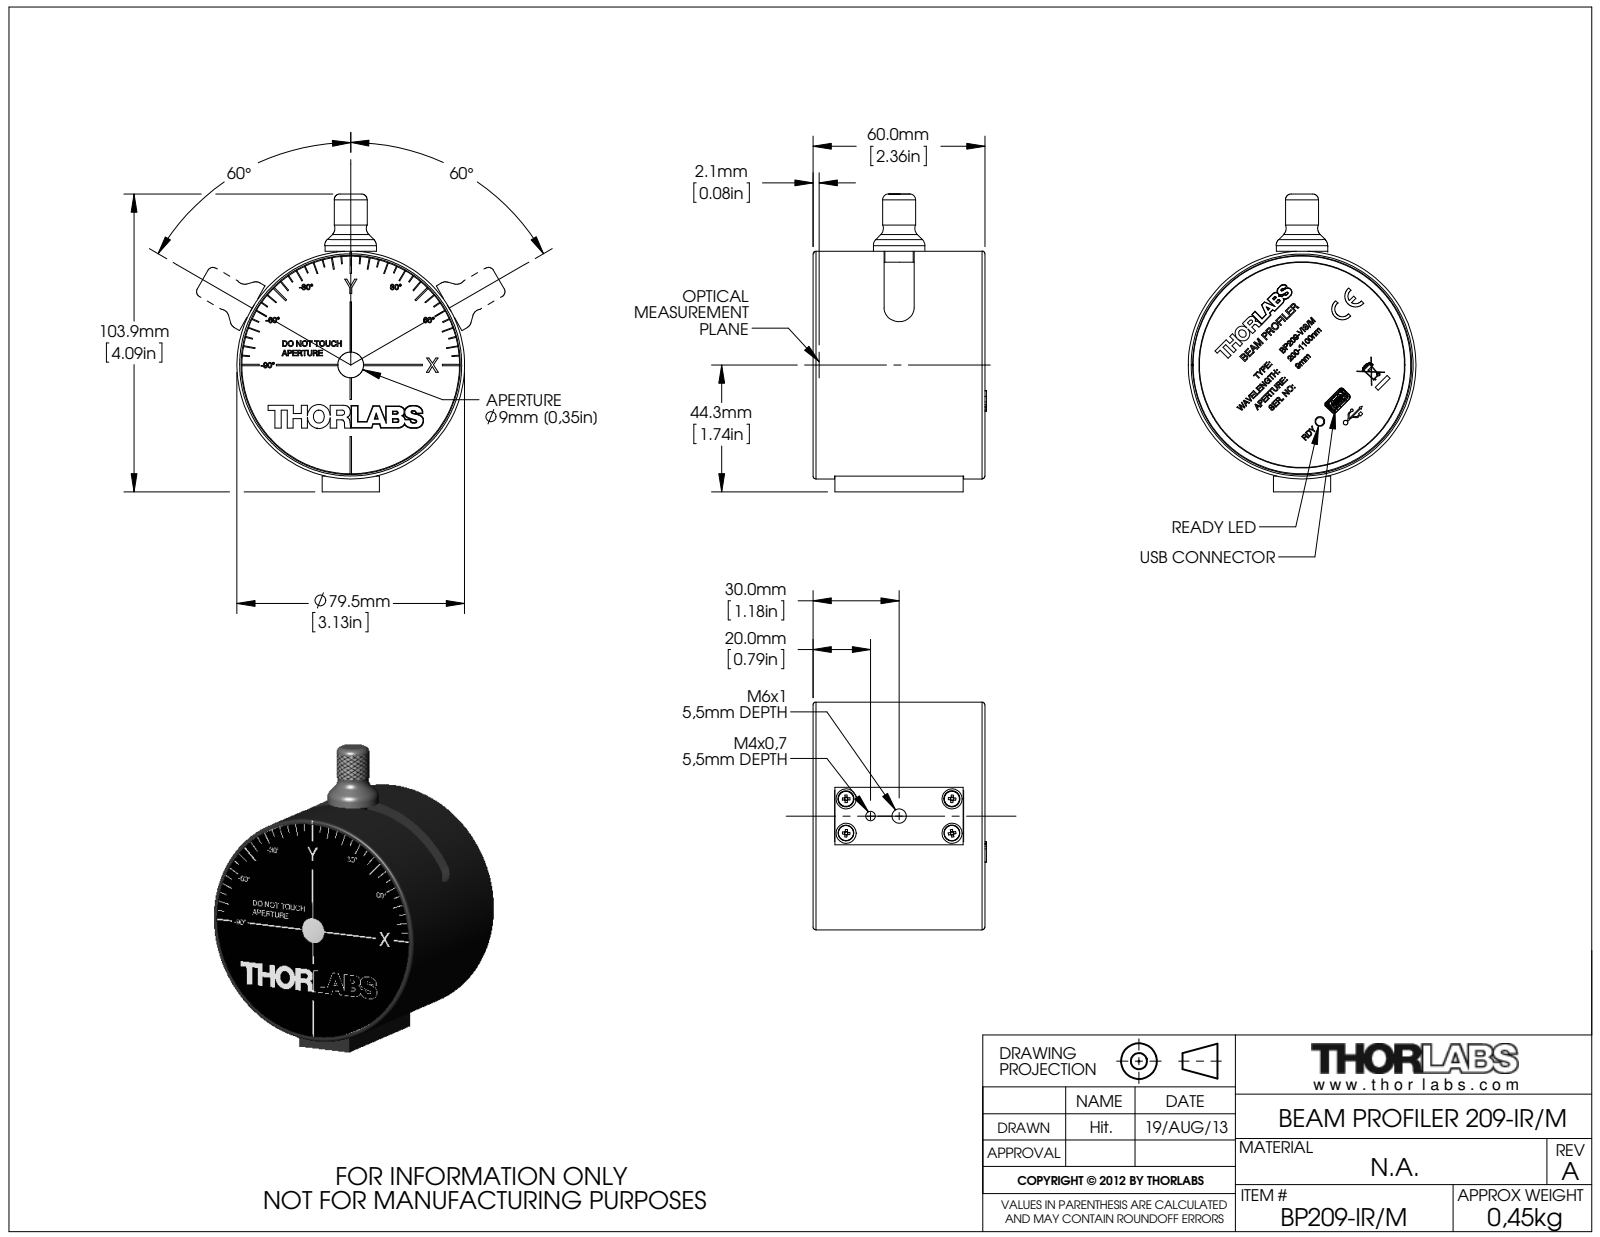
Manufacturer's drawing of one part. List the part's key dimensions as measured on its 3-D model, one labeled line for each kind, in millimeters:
Part name (STEP PRODUCT): 25067-E0W
STEP written by: SolidWorks 2012 (CONFIG_CONTROL_DESIGN)
Units: millimetres
Bodies: 14 solids, 3722 faces (2613 planar, 408 cylindrical, 701 other)
Overall size (bounding box): 103.95 × 79.5 × 60.5
Volume: 98 412 mm³ · Surface area: 99 234 mm²
Round holes (diameter × count): ⌀3.2 ×10, ⌀2.2 ×9, ⌀8 ×8, ⌀1.6 ×6, ⌀6.3 ×6, ⌀5 ×5, ⌀7 ×5, ⌀2.5 ×4, ⌀5.3 ×4, ⌀1 ×1, ⌀1.29 ×1, ⌀1.67 ×1
Round bosses / shafts (diameter × count): ⌀5.6 ×4, ⌀3 ×4, ⌀0.8 ×2, ⌀79.5 ×1, ⌀76 ×1, ⌀72.1 ×1, ⌀71.8 ×1, ⌀71.5 ×1
Partial cylindrical surfaces — rounded edges, fillets, slot ends (radius × count): R1.5 ×18, R4 ×16, R0.1 ×14, R0.2 ×14, R1 ×14, R0.3 ×9, R0.7 ×8, R5 ×8
Main face-to-face distances: 1, 59, 59.7, 60, 58, 0.7, 58.7, 0.5, 2, 1.5
Hole centre spacings: 23.73, 31, 43.84, 57.28, 27, 46.77, 27.01, 19.45
